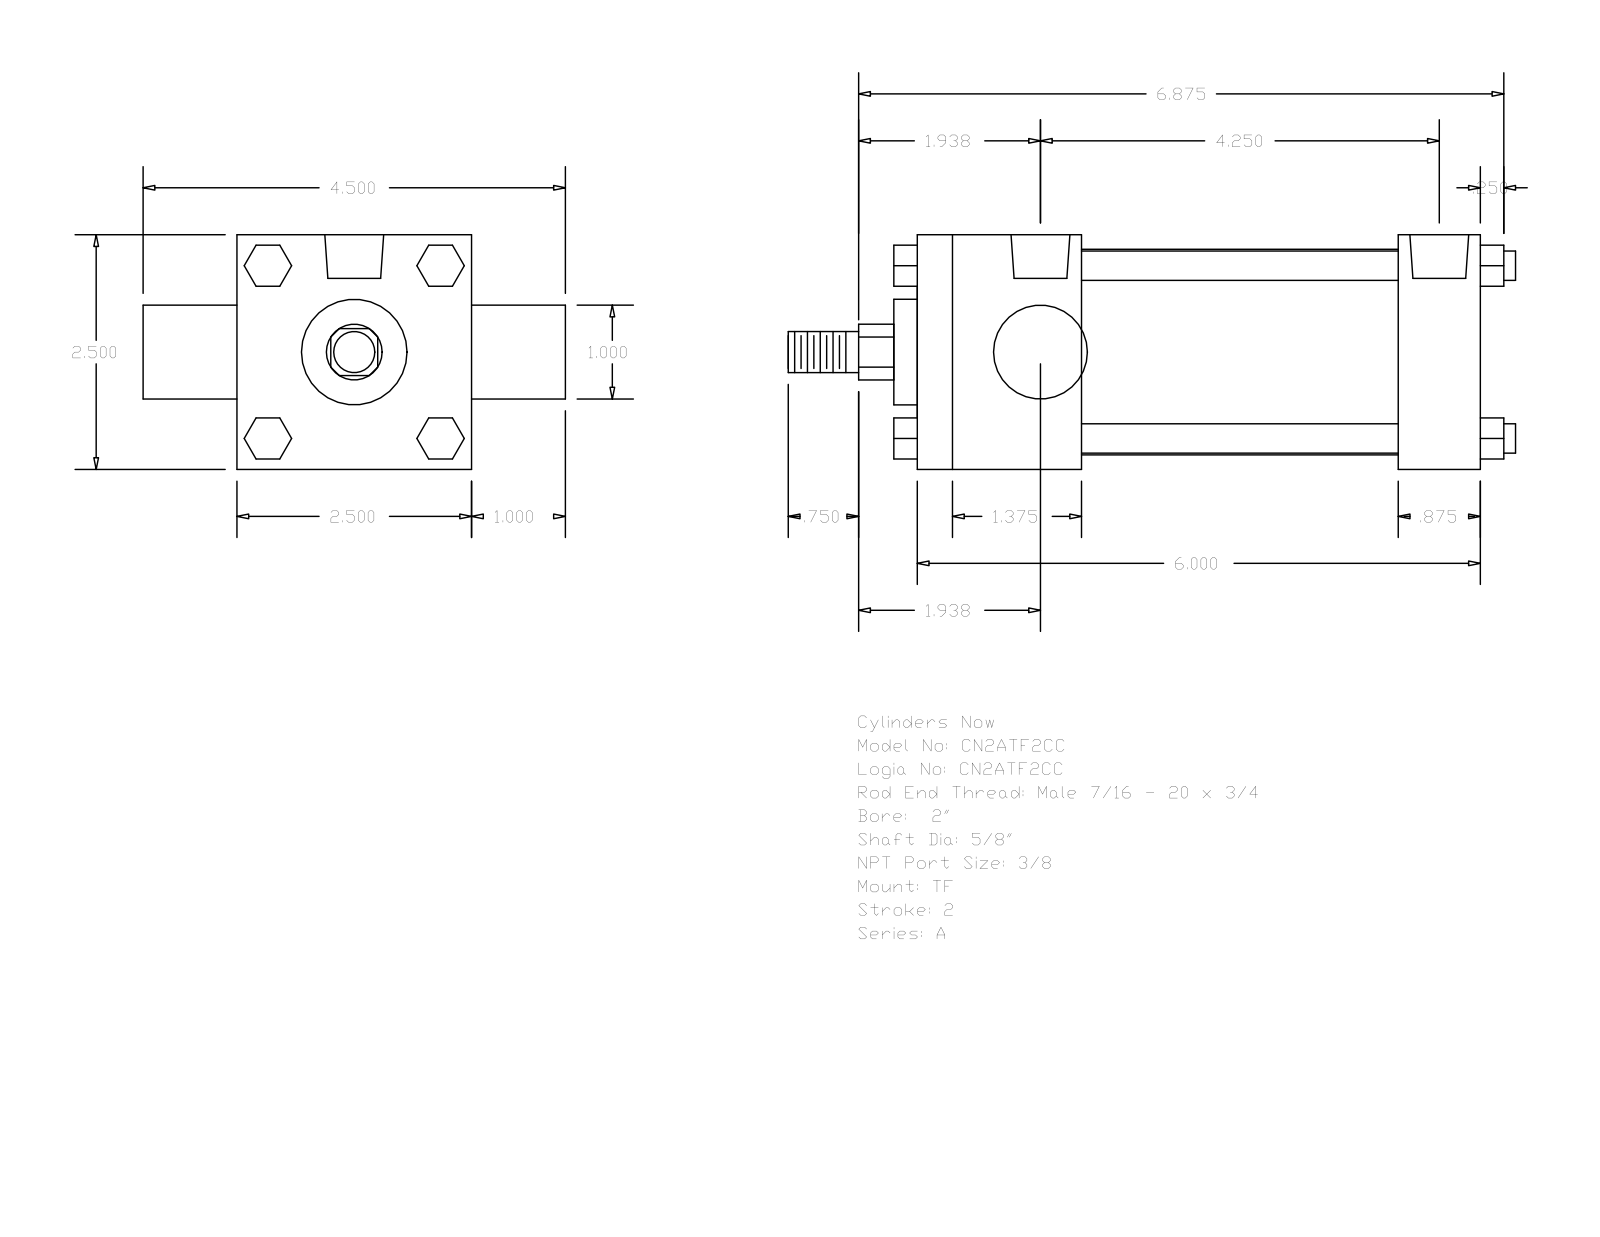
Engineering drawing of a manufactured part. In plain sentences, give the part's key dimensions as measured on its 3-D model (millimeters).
The part is named "A_TF__0200_0.625". Its 3-D file was written by "GSSL Pune (CONFIG_CONTROL_DESIGN)". It is 0 solids with 120 faces: 92 planar, 28 cylindrical and 0 other. Overall it measures 196.85 by 114.3 by 63.5 millimeters. Round holes: 3 of diameter 5.56, 2 of diameter 15.93. Round bosses or shafts: 4 of diameter 7.94, 1 of diameter 55.63, 1 of diameter 28.57, 1 of diameter 25.4, 1 of diameter 15.88, 1 of diameter 11.11. Partial cylindrical surfaces (rounded edges, fillets, slot ends): 1 of radius 7.54. The main face-to-face distances are 63.5, 152.4, 44.45, 130.17, 85.72, 107.95, 22.23, 25.4, 88.9, 50.8. The hole center spacings are 3.97, 3.98, 100, 103.97, 103.98, 107.95.
